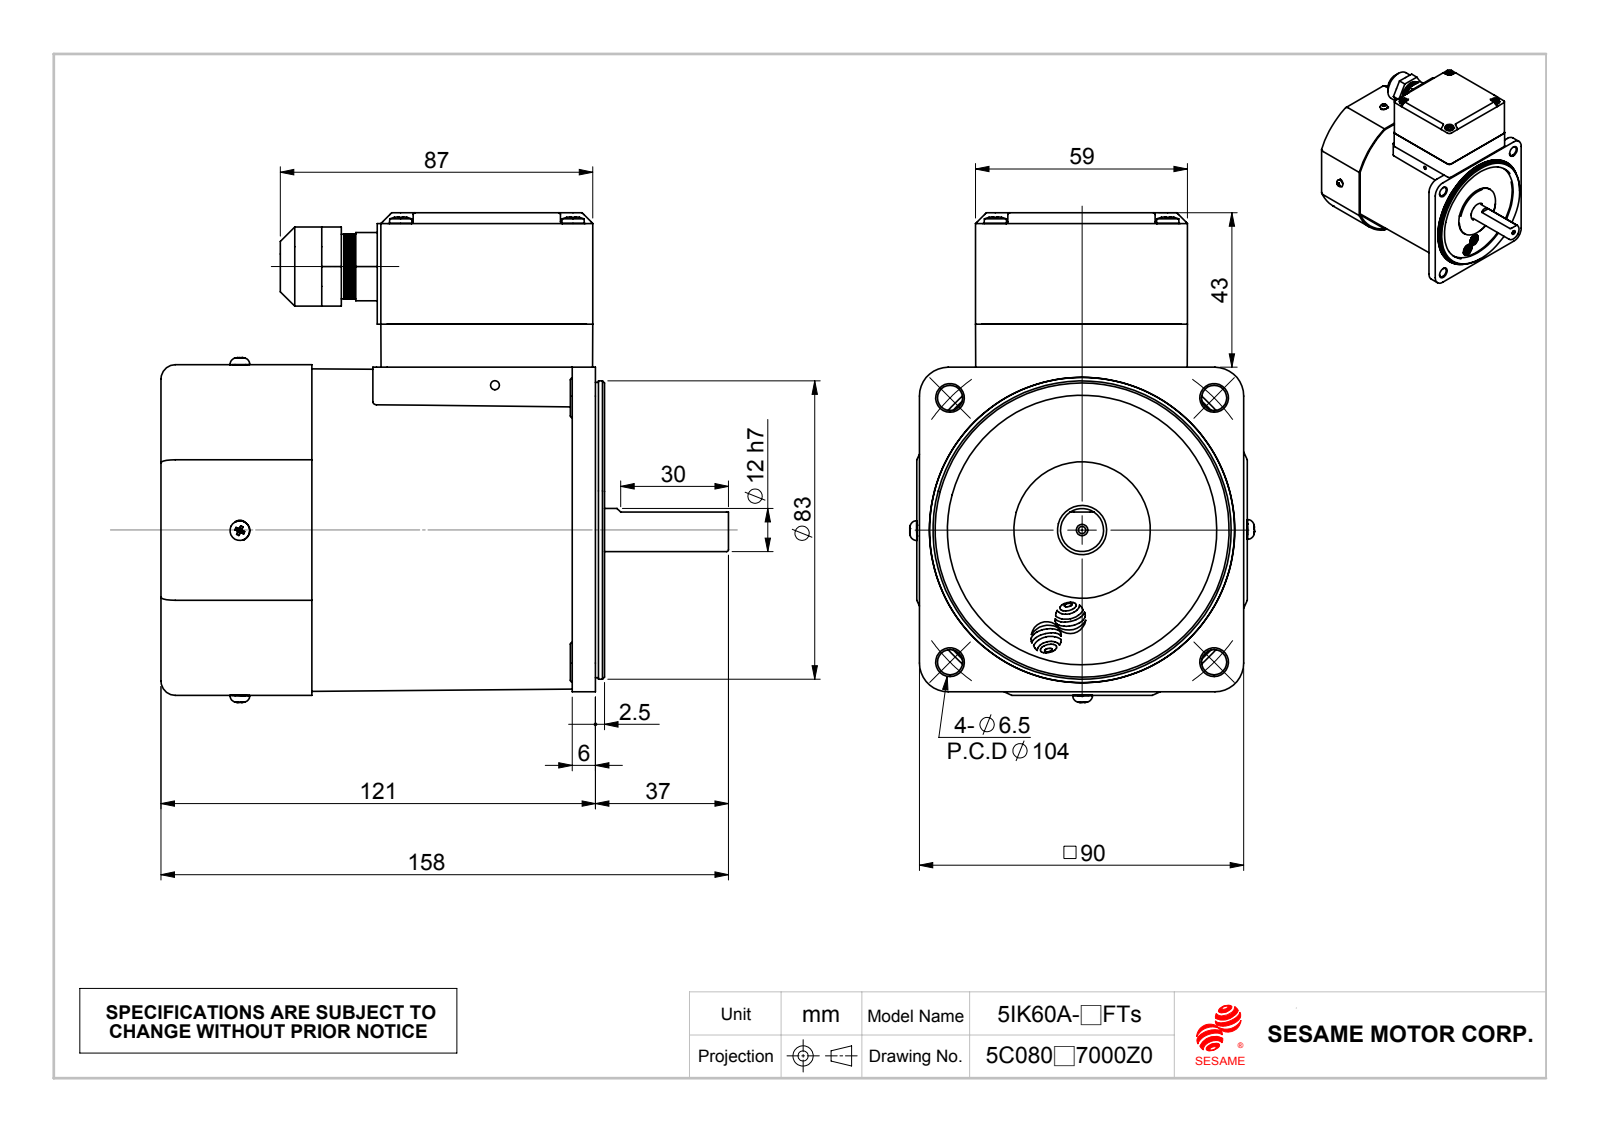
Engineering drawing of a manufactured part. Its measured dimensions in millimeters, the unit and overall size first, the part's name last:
Units: millimetres
Overall size (bounding box): 158 × 136.29 × 95.99
Round holes (diameter × count): ⌀2.5 ×5, ⌀3.3 ×4, ⌀3.5 ×4, ⌀3.9 ×4, ⌀4.3 ×4, ⌀7 ×4, ⌀2 ×1, ⌀6.5 ×1, ⌀11 ×1, ⌀12 ×1, ⌀13.7 ×1, ⌀14.5 ×1
Round bosses / shafts (diameter × count): ⌀3 ×8, ⌀6.3 ×4, ⌀5.5 ×4, ⌀85 ×1, ⌀84.22 ×1, ⌀83 ×1, ⌀82.2 ×1, ⌀47 ×1
Partial cylindrical surfaces — rounded edges, fillets, slot ends (radius × count): R0.3 ×16, R2 ×16, R1 ×10, R4 ×10, R0.5 ×8, R0.78 ×8, R1.5 ×8, R1.66 ×8
Main face-to-face distances: 1, 118.5, 12, 91, 102.5, 16, 118.4, 119.4, 117.5, 0.9
Hole centre spacings: 48, 52, 73.54, 11.67, 12.35, 12.7, 24.93, 25
Volume: 849 625 mm³ · Surface area: 136 125 mm²
Bodies: 16 solids, 2826 faces (330 planar, 1059 cylindrical, 1437 other)
Part name (STEP PRODUCT): 風扇蓋FC-9042-21; M560Ts-F; 60A; 成品180度 (+1 more)
STEP written by: SolidWorks 2010 (CONFIG_CONTROL_DESIGN)
